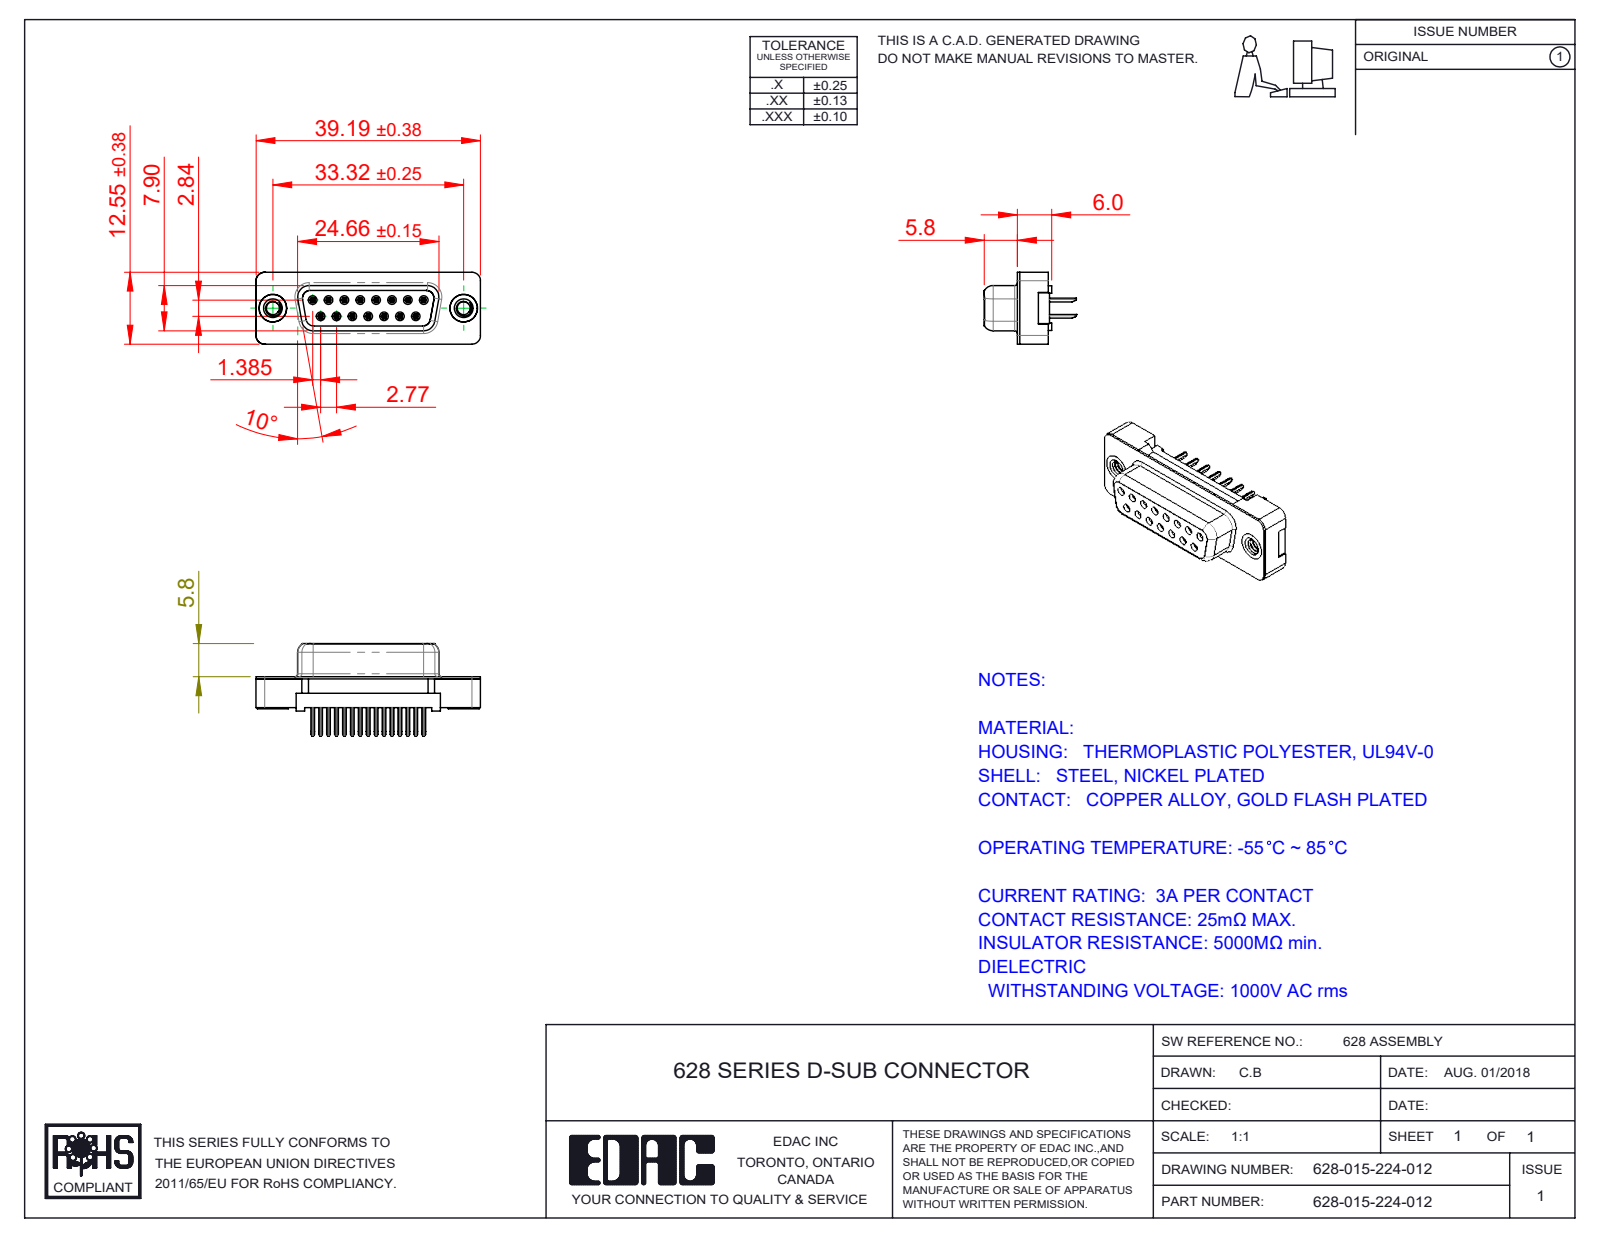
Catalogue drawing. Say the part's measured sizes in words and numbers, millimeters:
The part is named "628 Plastic Body Housing_15 Contacts; 628 PB Contact Row 2_24; 628 PB Contact Row 1_24; 628 PB Shell_15 Contacts (+2 more)". Its 3-D file was written by "SolidWorks 2020 (CONFIG_CONTROL_DESIGN)". It is 19 solids with 1355 faces: 564 planar, 344 cylindrical and 447 other. Overall it measures 39.2 by 16.1 by 12.55 millimeters. Its volume is 2 465 cubic millimeters and its surface area 6 031 square millimeters. Round holes: 15 of diameter 0.9, 2 of diameter 2.26, 2 of diameter 3.05, 2 of diameter 4, 2 of diameter 4.8, 2 of diameter 5. Round bosses or shafts: 2 of diameter 4.9. Partial cylindrical surfaces (rounded edges, fillets, slot ends): 60 of radius 0.25, 19 of radius 0.5, 15 of radius 0.3, 12 of radius 1.35, 8 of radius 1.5, 4 of radius 0.9, 4 of radius 1.6, 4 of radius 1.75. The main face-to-face distances are 0.4, 5.54, 2, 2.5, 6.2, 2.77, 0.68, 5.52, 2.68, 3.52. The hole center spacings are 3.16, 2.77, 5.54, 8.31, 11.08, 5.03, 5.04, 7.48.
